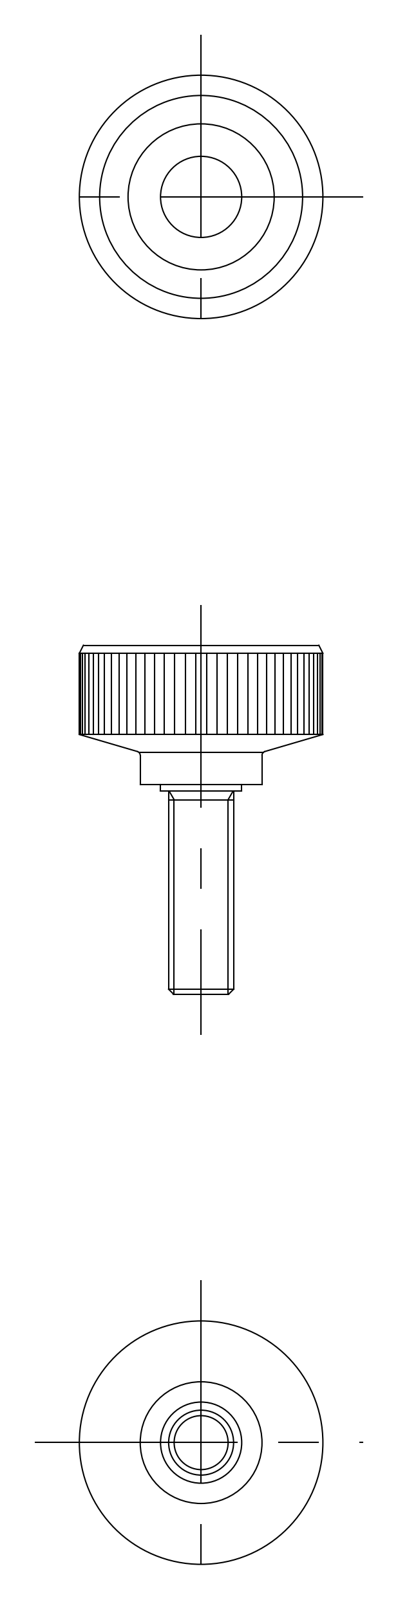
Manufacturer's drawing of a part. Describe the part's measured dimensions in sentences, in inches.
The part is named "screw; knob; KKM_30_M8_25_5514_36". Its 3-D file was written by "CADfix (AUTOMOTIVE_DESIGN)". It is 2 solids with 35 faces: 0 planar, 0 cylindrical and 35 other. Overall it measures 1.693 by 1.181 by 1.181 inches. Its volume is 0.488 cubic inches and its surface area 6.694 square inches.
